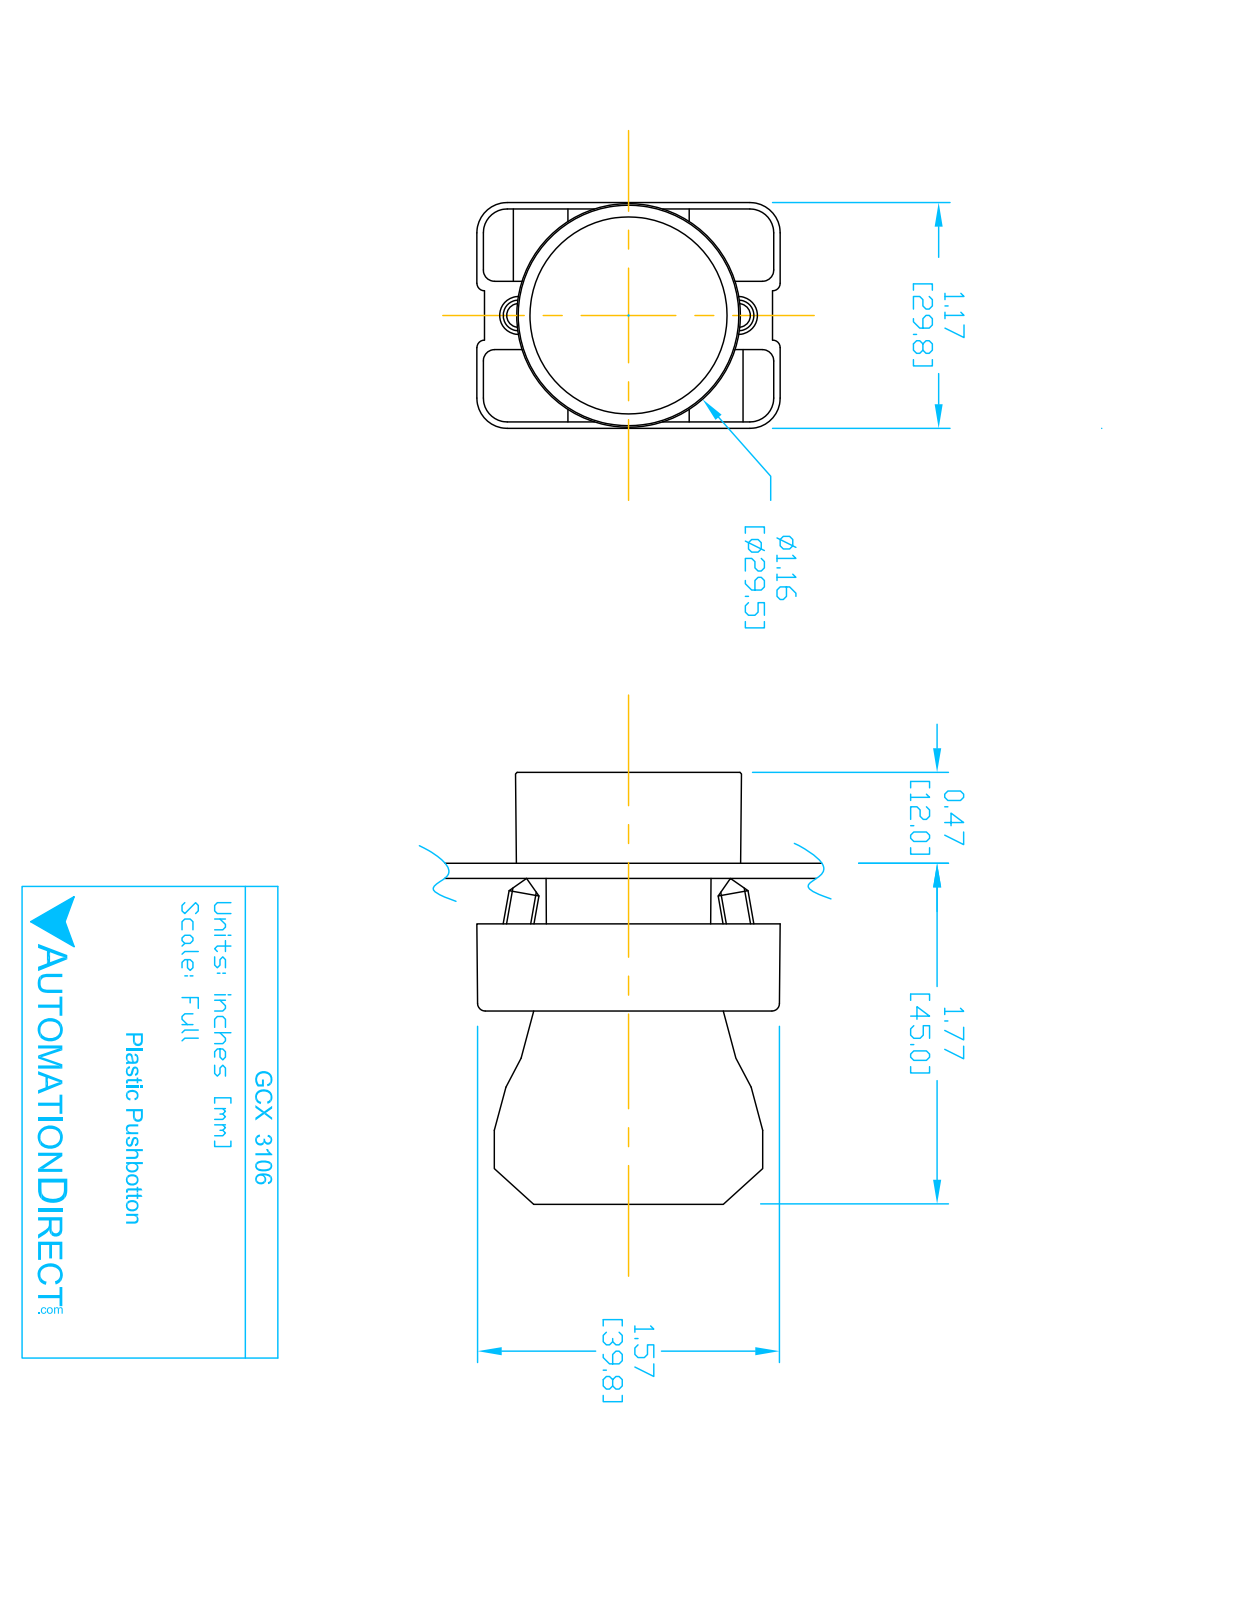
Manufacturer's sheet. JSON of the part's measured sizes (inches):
{"part_name": "GCX3106 OPERATOR; GCX3106; ECX3029-2; ecx1030", "step_written_by": "SolidWorks 2016 (AUTOMOTIVE_DESIGN)", "units": "inches", "bodies": {"solids": 6, "faces": 387, "planar": 224, "cylindrical": 136, "other": 27}, "overall_size": [2.217, 1.581, 1.177], "volume_in3": 1.741, "surface_area_in2": 27.14, "round_holes": [[0.079, 2], [0.124, 2], [0.13, 2], [0.087, 1], [0.197, 1], [0.787, 1], [0.878, 1], [0.888, 1], [1.024, 1]], "round_bosses_or_shafts": [[0.157, 2], [1.175, 1], [1.004, 1], [0.945, 1], [0.856, 1], [0.78, 1], [0.591, 1]], "partial_cylinders_radius": [[0.059, 24], [0.041, 12], [0.124, 12], [0.157, 12], [0.039, 4], [0.128, 2], [0.02, 1], [0.063, 1]], "face_to_face_distances": [0.72, 0.579, 0.033, 0.472, 1.193, 0.031, 0.689, 0.598, 1.161, 1.071], "hole_center_spacings": [0.236, 0.544, 0.472, 0.49]}
